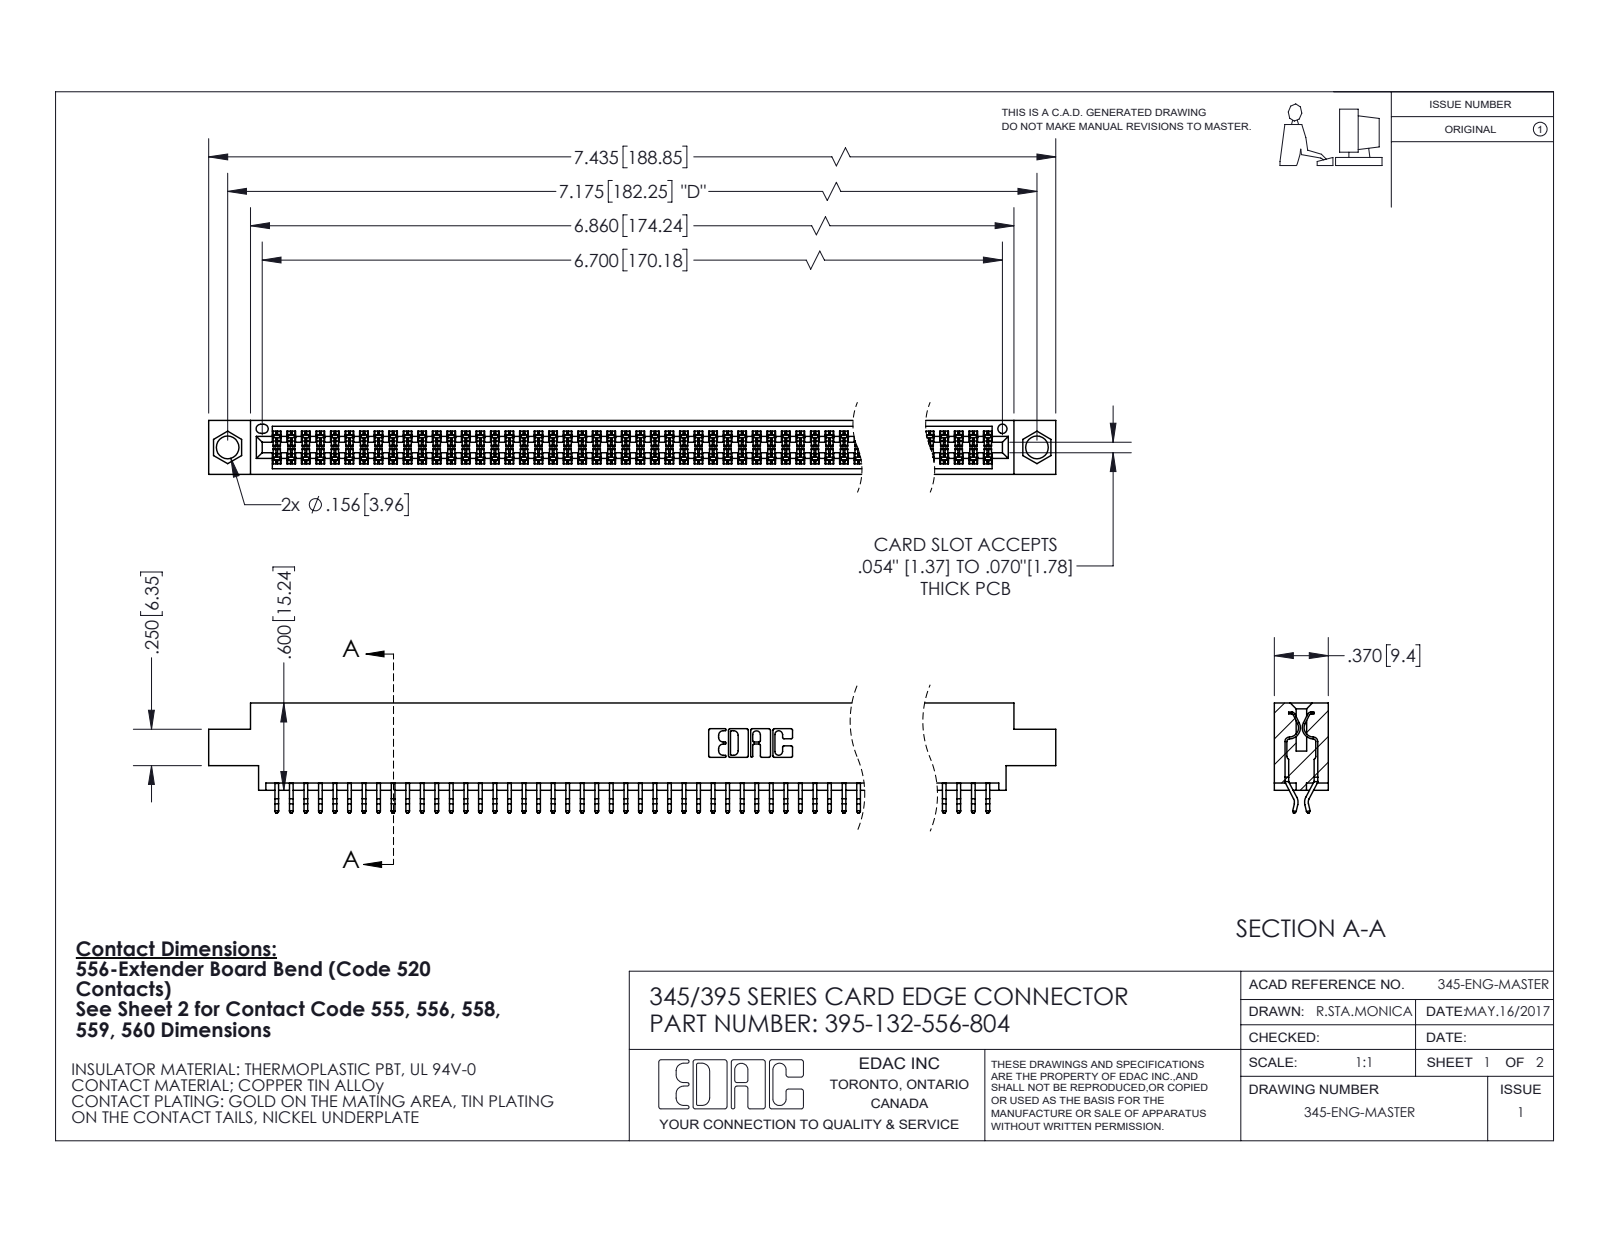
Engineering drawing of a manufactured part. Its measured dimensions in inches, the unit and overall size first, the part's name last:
Units: inches
Overall size (bounding box): 7.435 × 0.757 × 0.37
Round holes (diameter × count): ⌀0.156 ×2, ⌀0.064 ×1
Partial cylindrical surfaces — rounded edges, fillets, slot ends (radius × count): R0.006 ×264, R0.01 ×22, R0.007 ×6, R0.031 ×6, R0.026 ×3, R0.01 ×2, R0.014 ×2, R0.019 ×2
Main face-to-face distances: 0.072, 0.298, 0.37, 0.2, 0.025, 0.098, 0.272, 0.225, 0.175, 0.149
Hole centre spacings: 0.27, 6.939, 7.175
Volume: 1.119 in³ · Surface area: 42.56 in²
Bodies: 133 solids, 7536 faces (4982 planar, 2554 cylindrical, 0 other)
Part name (STEP PRODUCT): 345 Part_0.170 Offset - 0.156 Dia-TI; 345-292-001_556 Tail; 395-132-556-804
STEP written by: SolidWorks 2020 (CONFIG_CONTROL_DESIGN)
